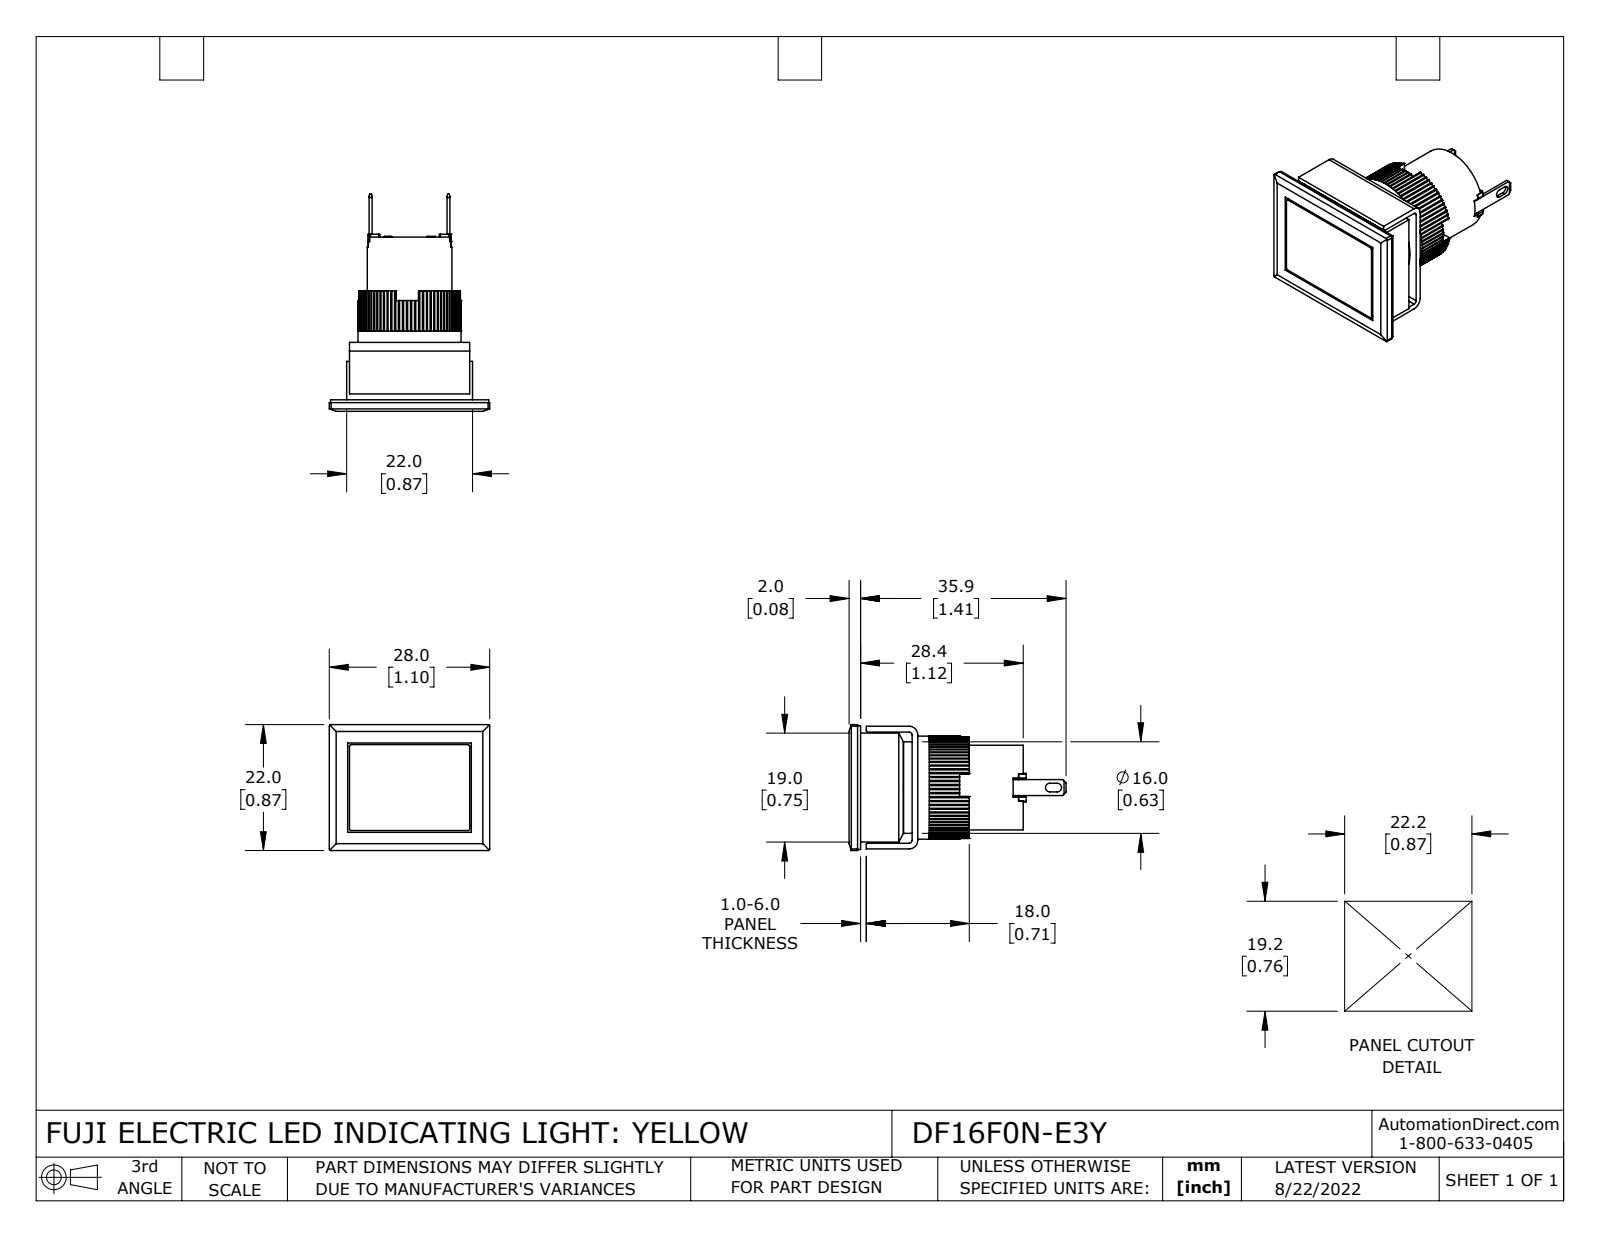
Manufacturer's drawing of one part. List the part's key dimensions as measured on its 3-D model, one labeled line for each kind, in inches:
Part name (STEP PRODUCT): DF16F0N-E3Y
STEP written by: SolidWorks 2021 (CONFIG_CONTROL_DESIGN)
Units: inches
Bodies: 10 solids, 495 faces (312 planar, 181 cylindrical, 2 other)
Overall size (bounding box): 1.492 × 1.102 × 0.866
Volume: 0.546 in³ · Surface area: 11.68 in²
Round holes (diameter × count): ⌀0.039 ×1, ⌀0.709 ×1
Round bosses / shafts (diameter × count): ⌀0.63 ×1, ⌀0.583 ×1
Partial cylindrical surfaces — rounded edges, fillets, slot ends (radius × count): R0.01 ×80, R0.008 ×12, R0.012 ×8, R0.02 ×2, R0.03 ×2, R0.059 ×2
Main face-to-face distances: 0.059, 0.374, 0.142, 0.02, 0.039, 0.315, 0.232, 0.083, 0.079, 0.756
